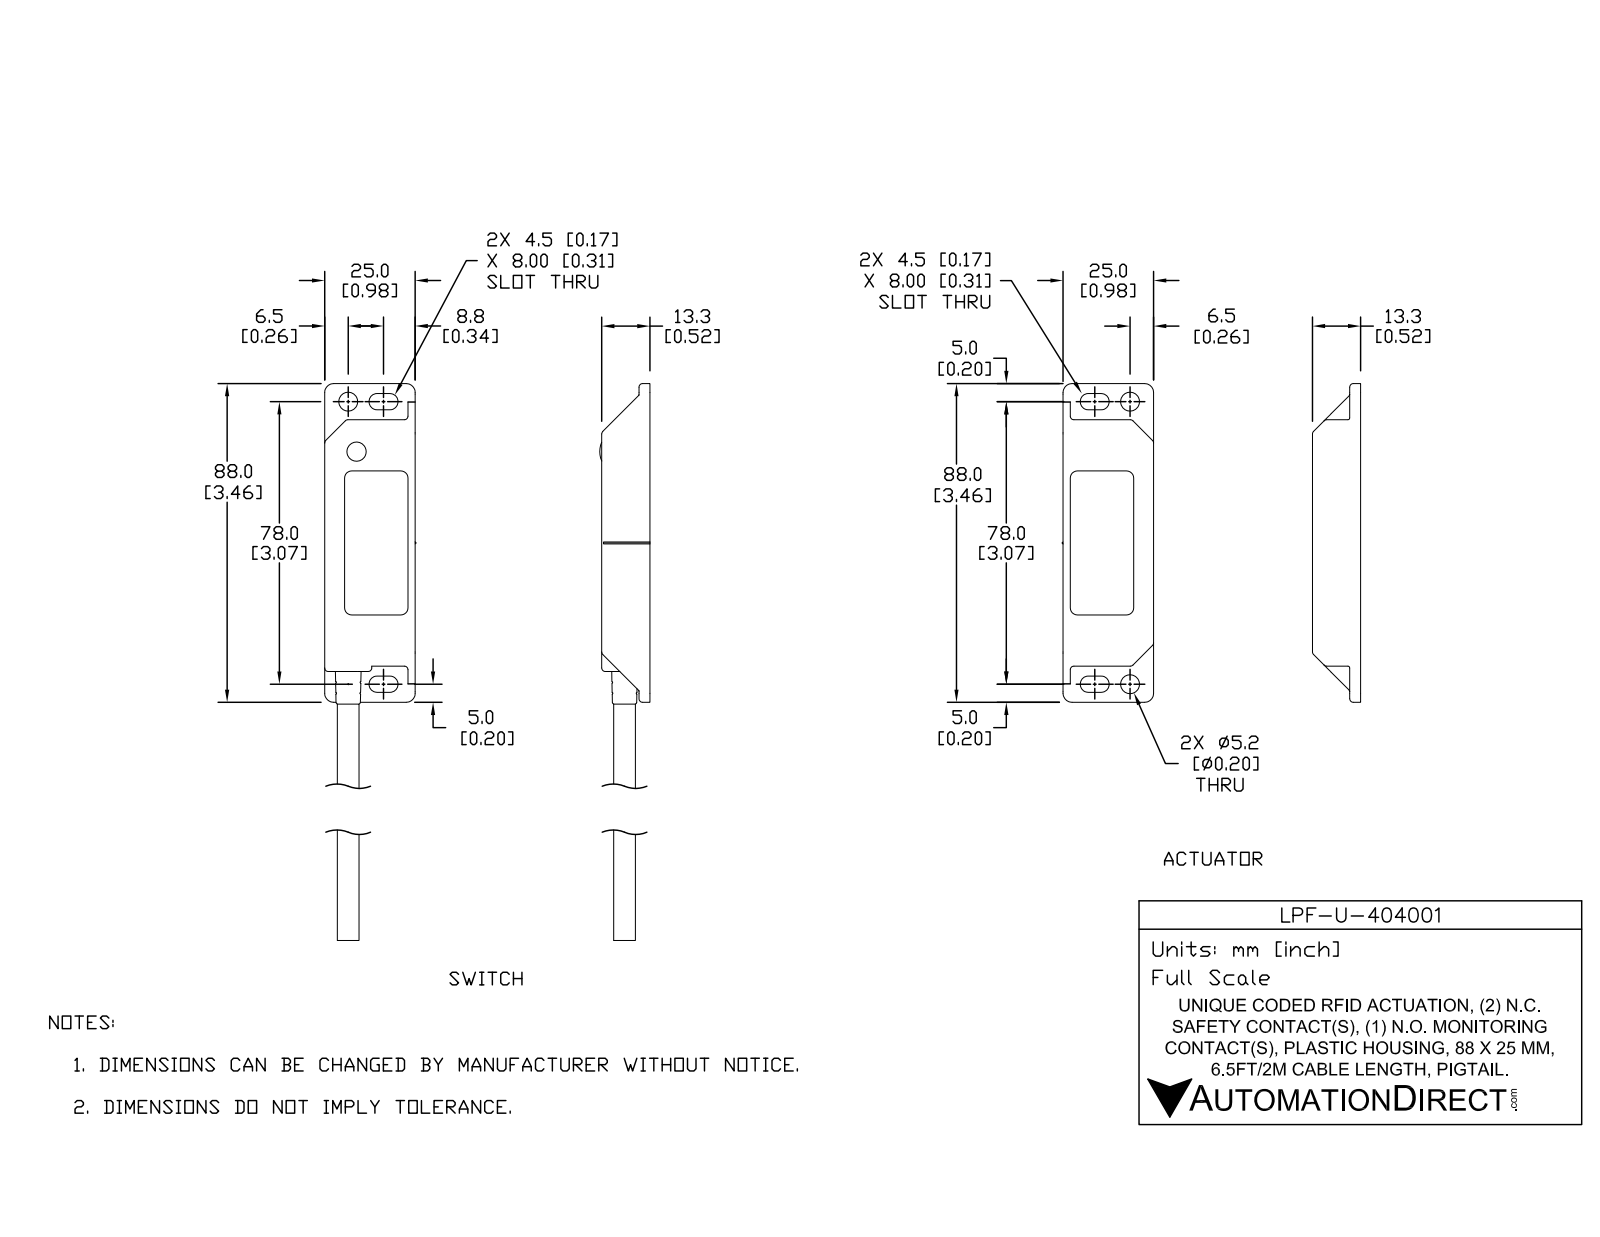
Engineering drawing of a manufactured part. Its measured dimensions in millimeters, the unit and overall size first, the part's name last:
Units: millimetres
Overall size (bounding box): 224.8 × 50.6 × 13.8
Round holes (diameter × count): ⌀5 ×4, ⌀5.2 ×4, ⌀3 ×1, ⌀4.4 ×1, ⌀5.4 ×1, ⌀5.9 ×1, ⌀7 ×1
Round bosses / shafts (diameter × count): ⌀2 ×4, ⌀4.9 ×2, ⌀2.3 ×2, ⌀8.6 ×1, ⌀7.6 ×1, ⌀7.1 ×1, ⌀6 ×1, ⌀5.3 ×1
Partial cylindrical surfaces — rounded edges, fillets, slot ends (radius × count): R0.5 ×116, R1 ×49, R2 ×10, R2.3 ×8, R2.5 ×8, R0.3 ×6, R4.8 ×1
Main face-to-face distances: 1.7, 11.2, 2, 9.5, 1.5, 1.8, 12.9, 11.3, 13, 25.1
Hole centre spacings: 19, 27.9, 30.2, 32.4, 37.6, 39.9, 45.3, 48.1
Volume: 26 840 mm³ · Surface area: 30 250 mm²
Bodies: 11 solids, 1058 faces (401 planar, 303 cylindrical, 354 other)
Part name (STEP PRODUCT): LPF-U-404001_1; LPF-U-404001; LPF-U-404001_2
STEP written by: SolidWorks 2017 (AUTOMOTIVE_DESIGN)
